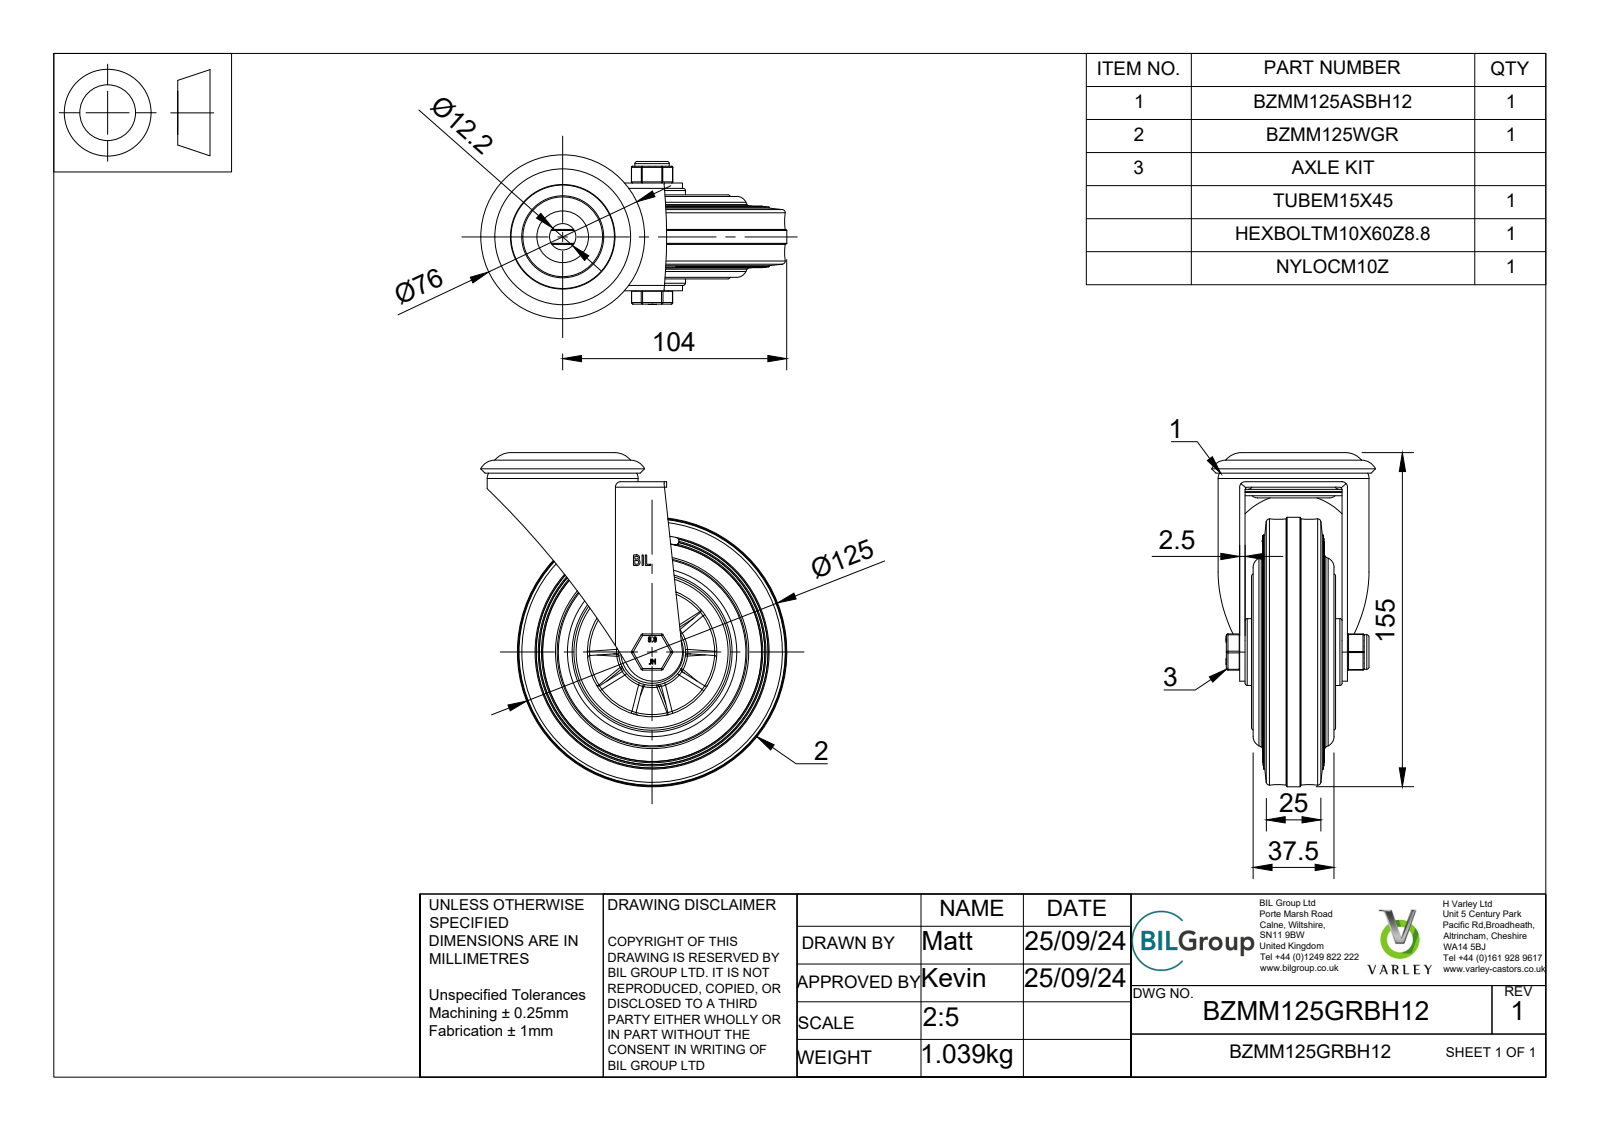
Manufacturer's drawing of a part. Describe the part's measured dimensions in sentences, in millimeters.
The part is named "BZMM125GRBH12 v3; BZMM125ASBH12 v1; ZINC PLATED, PRESSED STEEL HEAD; ZINC PLATED, PRESSED STEEL FORKS (+8 more)". Its 3-D file was written by "Autodesk Translation Framework v13.20.0.188 (AUTOMOTIVE_DESIGN)". It is 8 solids with 657 faces: 139 planar, 116 cylindrical and 402 other. Overall it measures 155 by 142 by 76 millimeters. Its volume is 392 436 cubic millimeters and its surface area 129 400 square millimeters. Round holes: 1 of diameter 10, 1 of diameter 10.2, 1 of diameter 12, 1 of diameter 12.2, 1 of diameter 15.2, 1 of diameter 60, 1 of diameter 65, 1 of diameter 67.5, 1 of diameter 72, 1 of diameter 72.5. Round bosses or shafts: 1 of diameter 125, 1 of diameter 70, 1 of diameter 49.5, 1 of diameter 38, 1 of diameter 31, 1 of diameter 24, 1 of diameter 21.31, 1 of diameter 16. Partial cylindrical surfaces (rounded edges, fillets, slot ends): 18 of radius 0.5, 12 of radius 0.75, 4 of radius 1.25, 2 of radius 2.5, 1 of radius 13.5, 1 of radius 253.62, 1 of radius 408.21. The main face-to-face distances are 2.5, 47.5, 6.5, 45, 3, 50, 42, 3.75, 5.5, 44.5.
